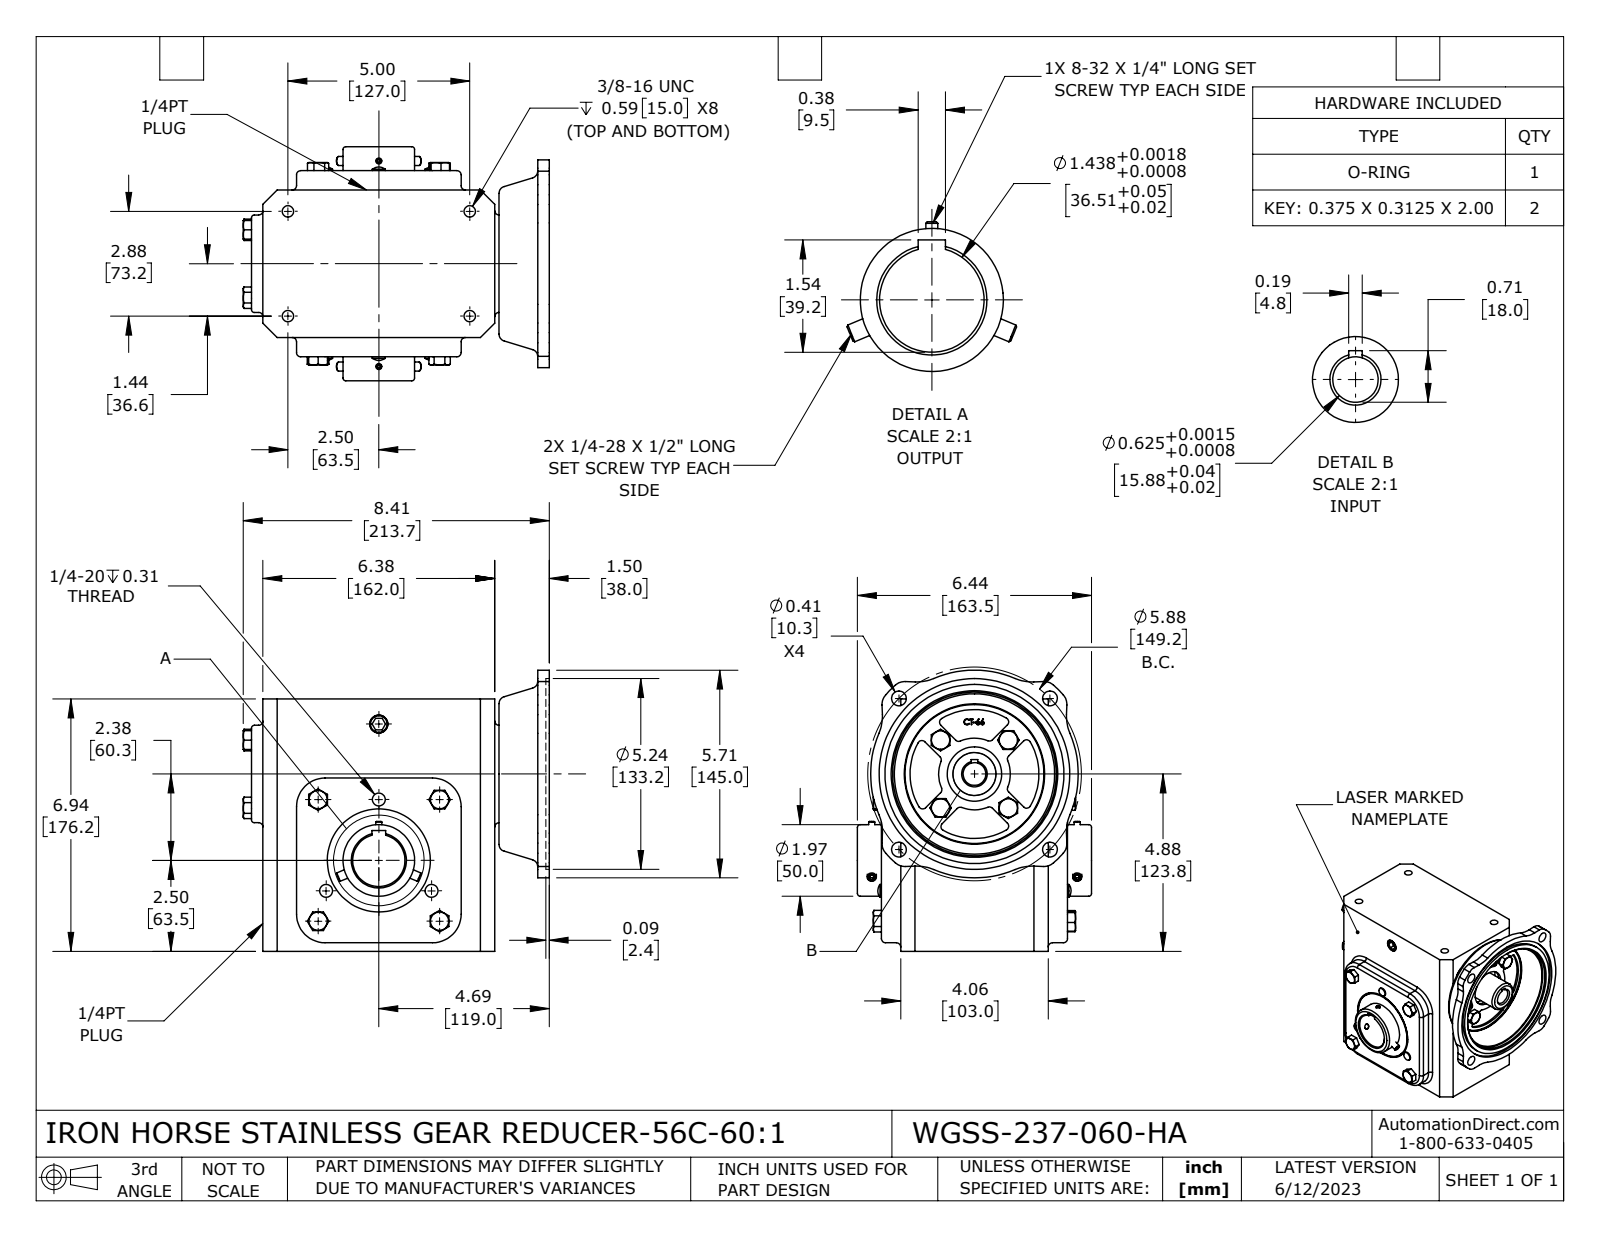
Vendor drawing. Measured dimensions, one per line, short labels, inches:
name: WGSS-237-060-HA
written by: SolidWorks 2021 (CONFIG_CONTROL_DESIGN)
unit: in
bodies: 7 solids, 670 faces (287 planar, 195 cylindrical, 188 other)
size: 8.412 × 7.729 × 6.437
volume: 204.5 in³; area: 348.1 in²
holes: 4× ⌀0.213, 4× ⌀0.313, 4× ⌀0.406, 2× ⌀0.136, 1× ⌀0.625, 1× ⌀0.866, 1× ⌀1.437, 1× ⌀1.441, 1× ⌀1.496, 1× ⌀1.772, 1× ⌀3.819, 1× ⌀4.5
bosses: 4× ⌀0.25, 3× ⌀0.354, 2× ⌀0.164, 1× ⌀4.921, 1× ⌀2.835, 1× ⌀1.969, 1× ⌀1.181
rounds: 40× R0.118, 12× R0.394, 8× R1.181, 4× R0.079, 4× R0.787, 1× R0.984, 1× R1.772, 1× R2.854
face distances: 0.531, 4.587, 6.937, 0.315, 4.055, 6.378, 5.118, 7.874, 1.181, 6.693
hole spacings: 2.858, 2.937, 4.944, 5.65, 2.88, 4.154, 4.154, 5
